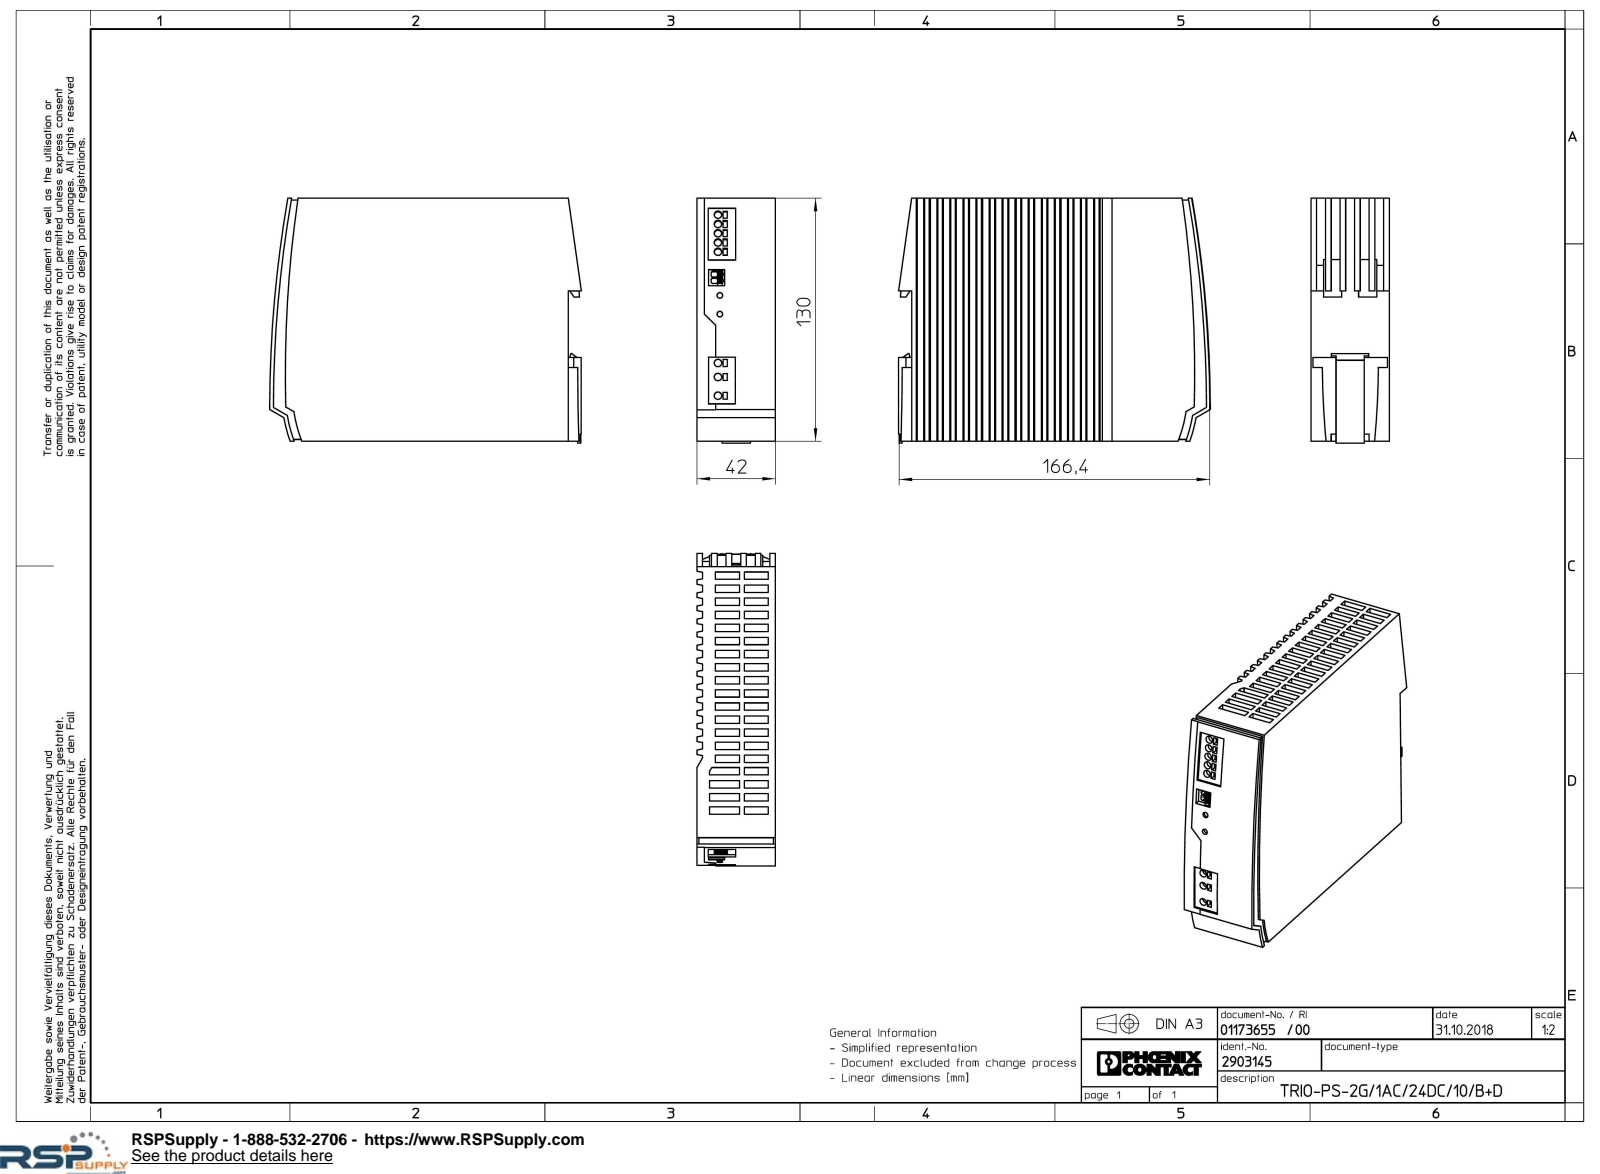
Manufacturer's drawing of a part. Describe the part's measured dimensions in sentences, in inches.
The part is named "TRIO_PS_2G_1AC_24DC_10_B_D-select". Its 3-D file was written by "Creo Elements/Direct Modeling 20.1A 29-Sep-2018 (C) Parametric Technology GmbH (AUTOMOTIVE_DESIGN)". It is 1 solid with 694 faces: 647 planar, 43 cylindrical and 4 other. Overall it measures 6.575 by 5.157 by 1.654 inches. Its volume is 50.44 cubic inches and its surface area 133.8 square inches. Round holes: 8 of diameter 0.157, 2 of diameter 0.118. Partial cylindrical surfaces (rounded edges, fillets, slot ends): 2 of radius 0.022, 2 of radius 0.024, 2 of radius 0.041, 2 of radius 0.041, 2 of radius 16.929, 1 of radius 1.575, 1 of radius 1.815, 1 of radius 2.722. The main face-to-face distances are 0.118, 1.654, 0.543, 1.086, 1.535, 1.629, 0.271, 0.272, 2.172, 0.814. The hole center spacings are 0.197, 0.394, 0.295, 0.395, 0.59, 0.591, 0.689, 0.787.
